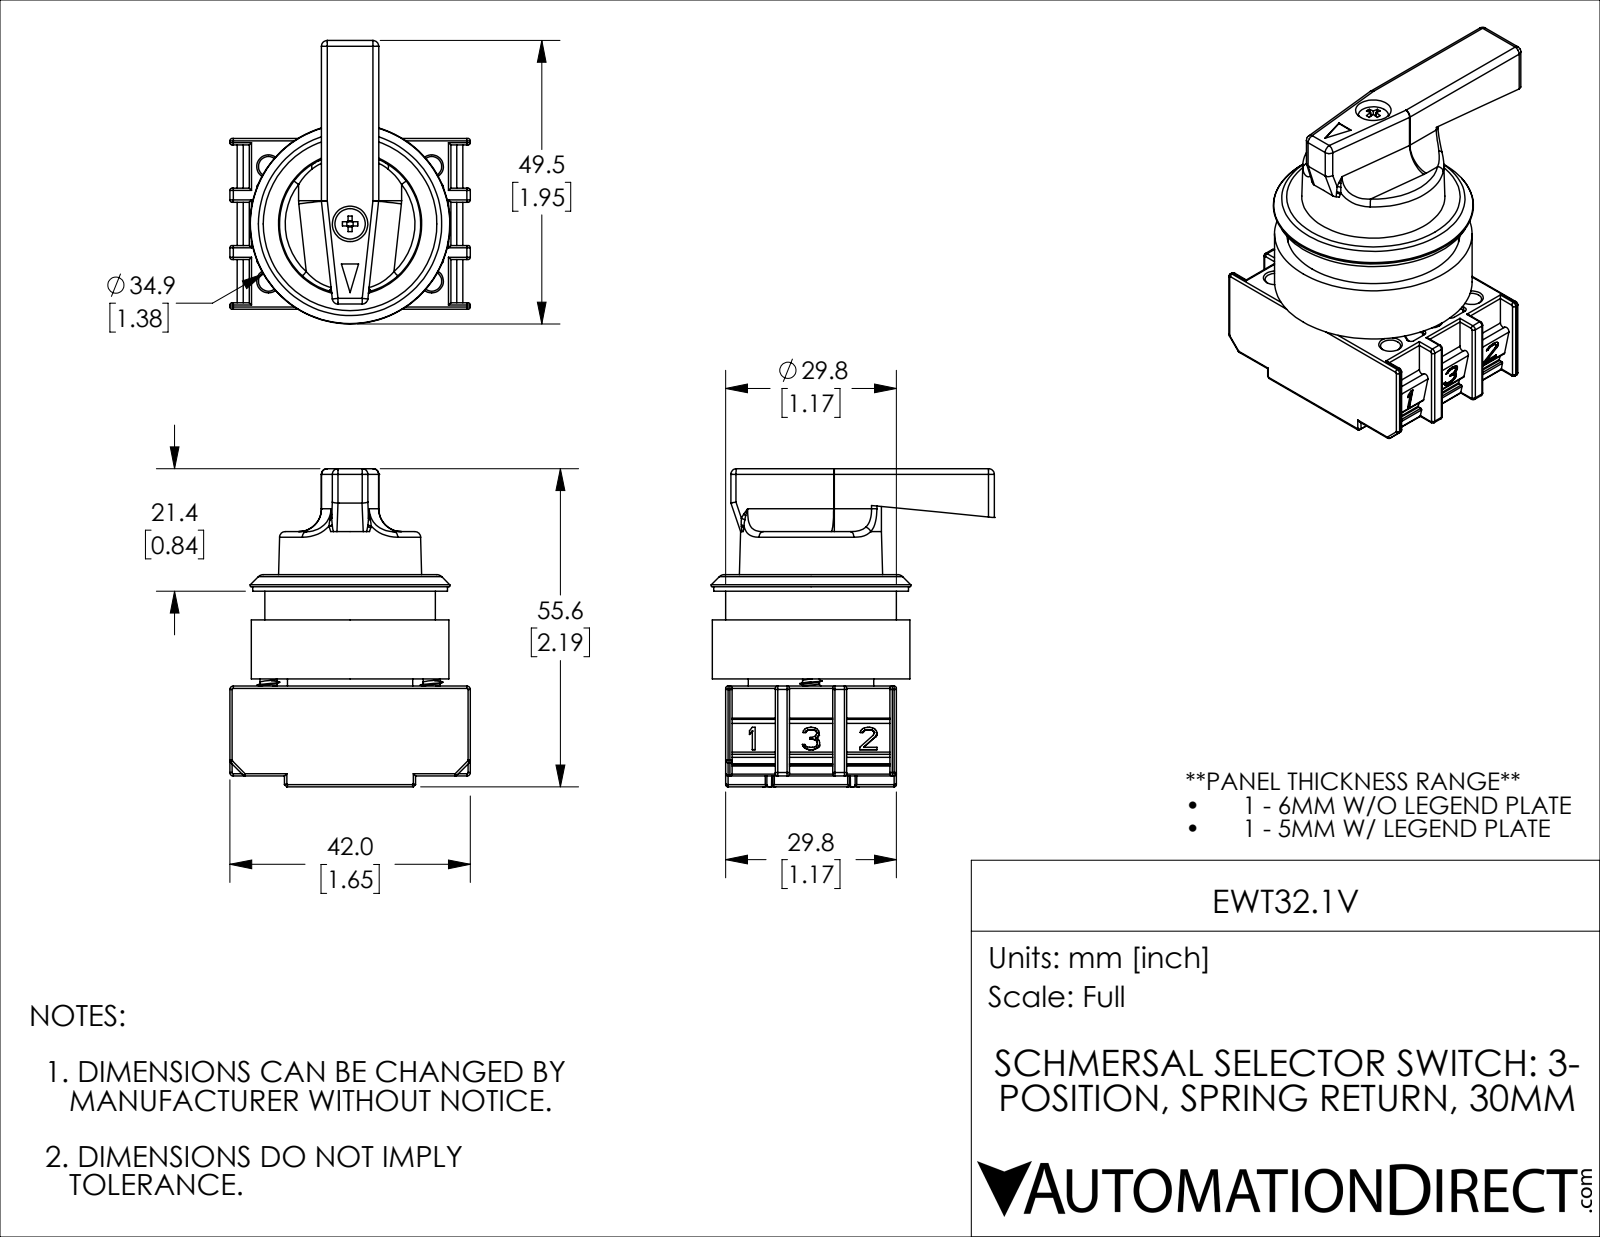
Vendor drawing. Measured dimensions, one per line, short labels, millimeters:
name: EWT32.1V
written by: SolidWorks 2019 (CONFIG_CONTROL_DESIGN)
unit: mm
bodies: 5 solids, 1738 faces (639 planar, 598 cylindrical, 501 other)
size: 55.55 × 49.47 × 42
volume: 29 601 mm³; area: 26 700 mm²
holes: 6× ⌀3.5, 6× ⌀5.15, 4× ⌀2, 4× ⌀5, 2× ⌀1.65, 2× ⌀1.95, 1× ⌀6.2, 1× ⌀9.15, 1× ⌀11, 1× ⌀14, 1× ⌀19, 1× ⌀22
bosses: 4× ⌀4.8, 2× ⌀2.93, 1× ⌀34.5, 1× ⌀34, 1× ⌀29.8, 1× ⌀25.5, 1× ⌀21.9, 1× ⌀18.5
rounds: 120× R0.4, 48× R0.3, 40× R1, 28× R0.2, 14× R0.5, 8× R0.6, 6× R0.8, 4× R4
face distances: 16.1, 17.35, 18.85, 29.8, 2.1, 18.2, 10, 18.3, 37.05, 34.95
hole spacings: 14.33, 3.03, 4.24, 6, 6.26, 7.07, 9.01, 10
